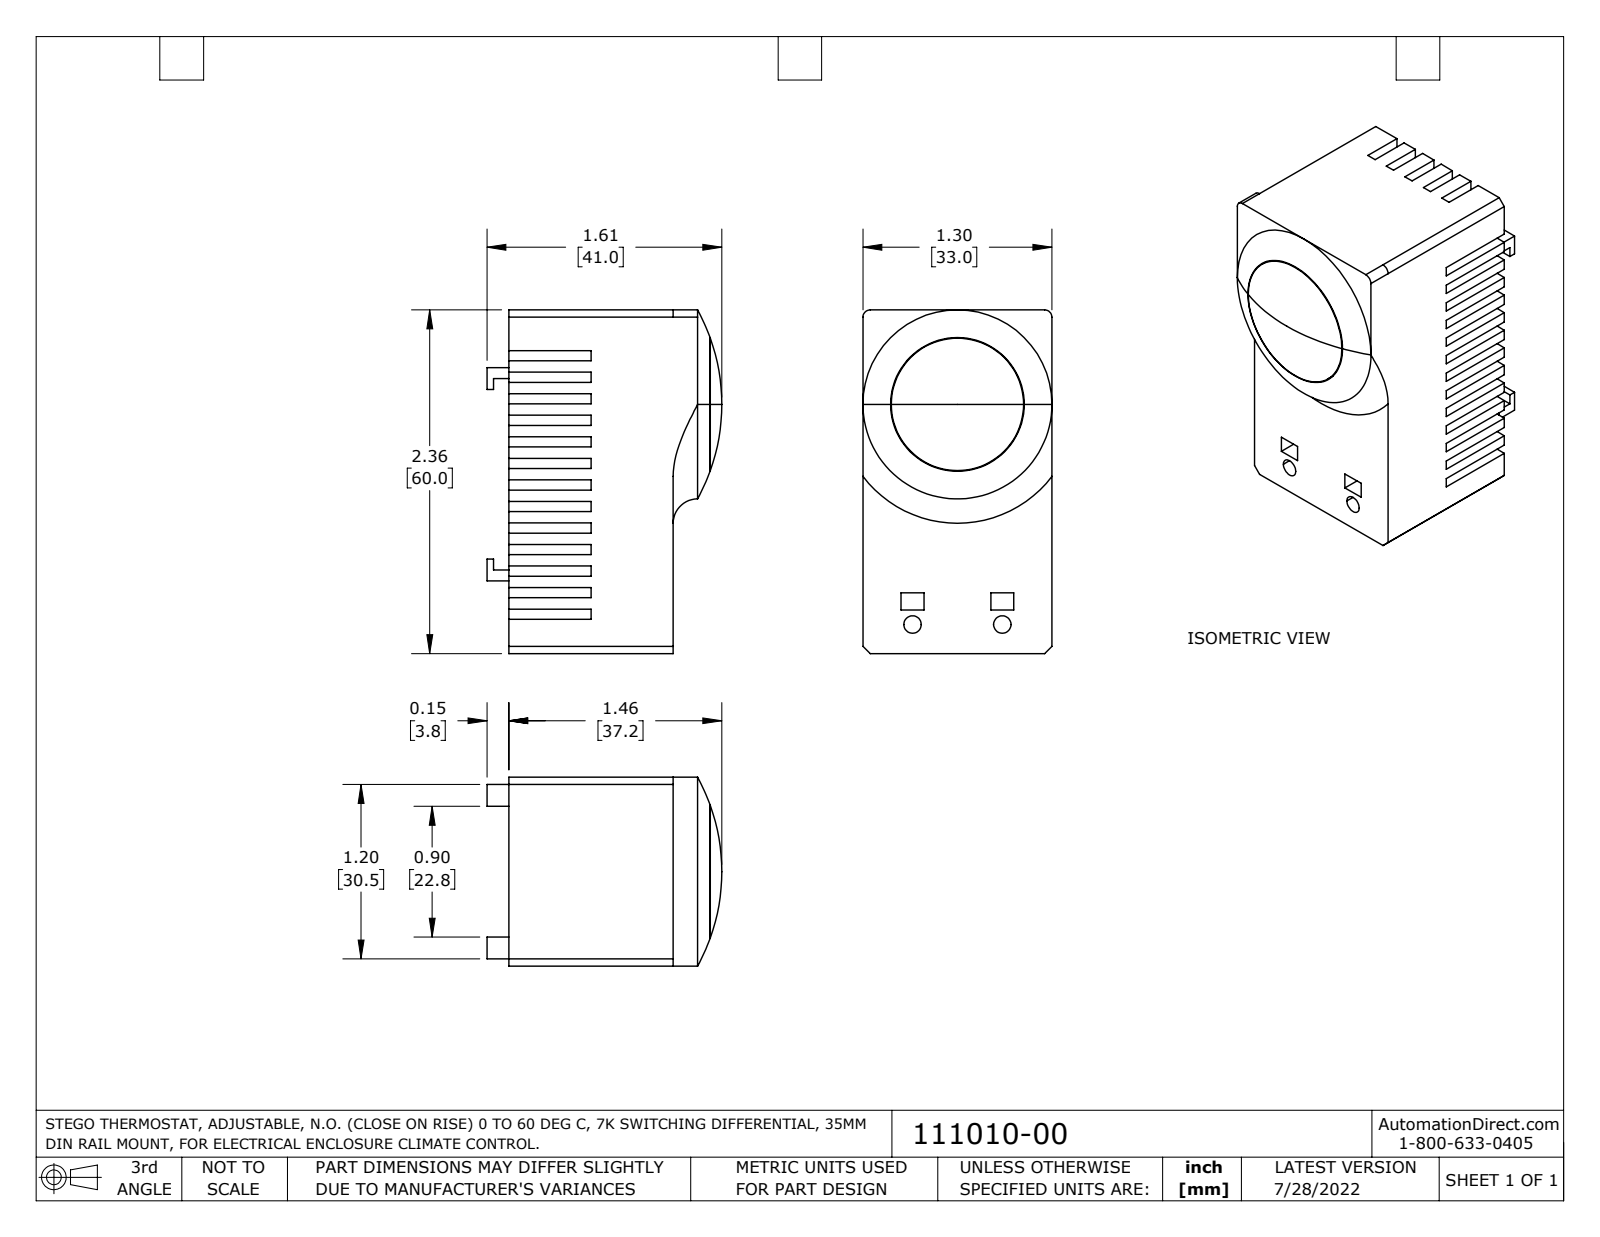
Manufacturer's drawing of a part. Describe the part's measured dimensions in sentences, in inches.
The part is named "111010-00_Default". Its 3-D file was written by "SolidWorks 2021 (CONFIG_CONTROL_DESIGN)". It is 1 solid with 198 faces: 183 planar, 10 cylindrical and 5 other. Overall it measures 2.362 by 1.614 by 1.299 inches. Its volume is 3.737 cubic inches and its surface area 19.92 square inches. Round holes: 2 of diameter 0.12, 1 of diameter 0.919. Round bosses or shafts: 1 of diameter 0.909. Partial cylindrical surfaces (rounded edges, fillets, slot ends): 2 of radius 0.05. The main face-to-face distances are 1.299, 0.148, 0.07, 2.362, 0.296, 1.13, 0.444, 0.592, 0.078, 0.218. The hole center spacings are 1.544, 0.617.
